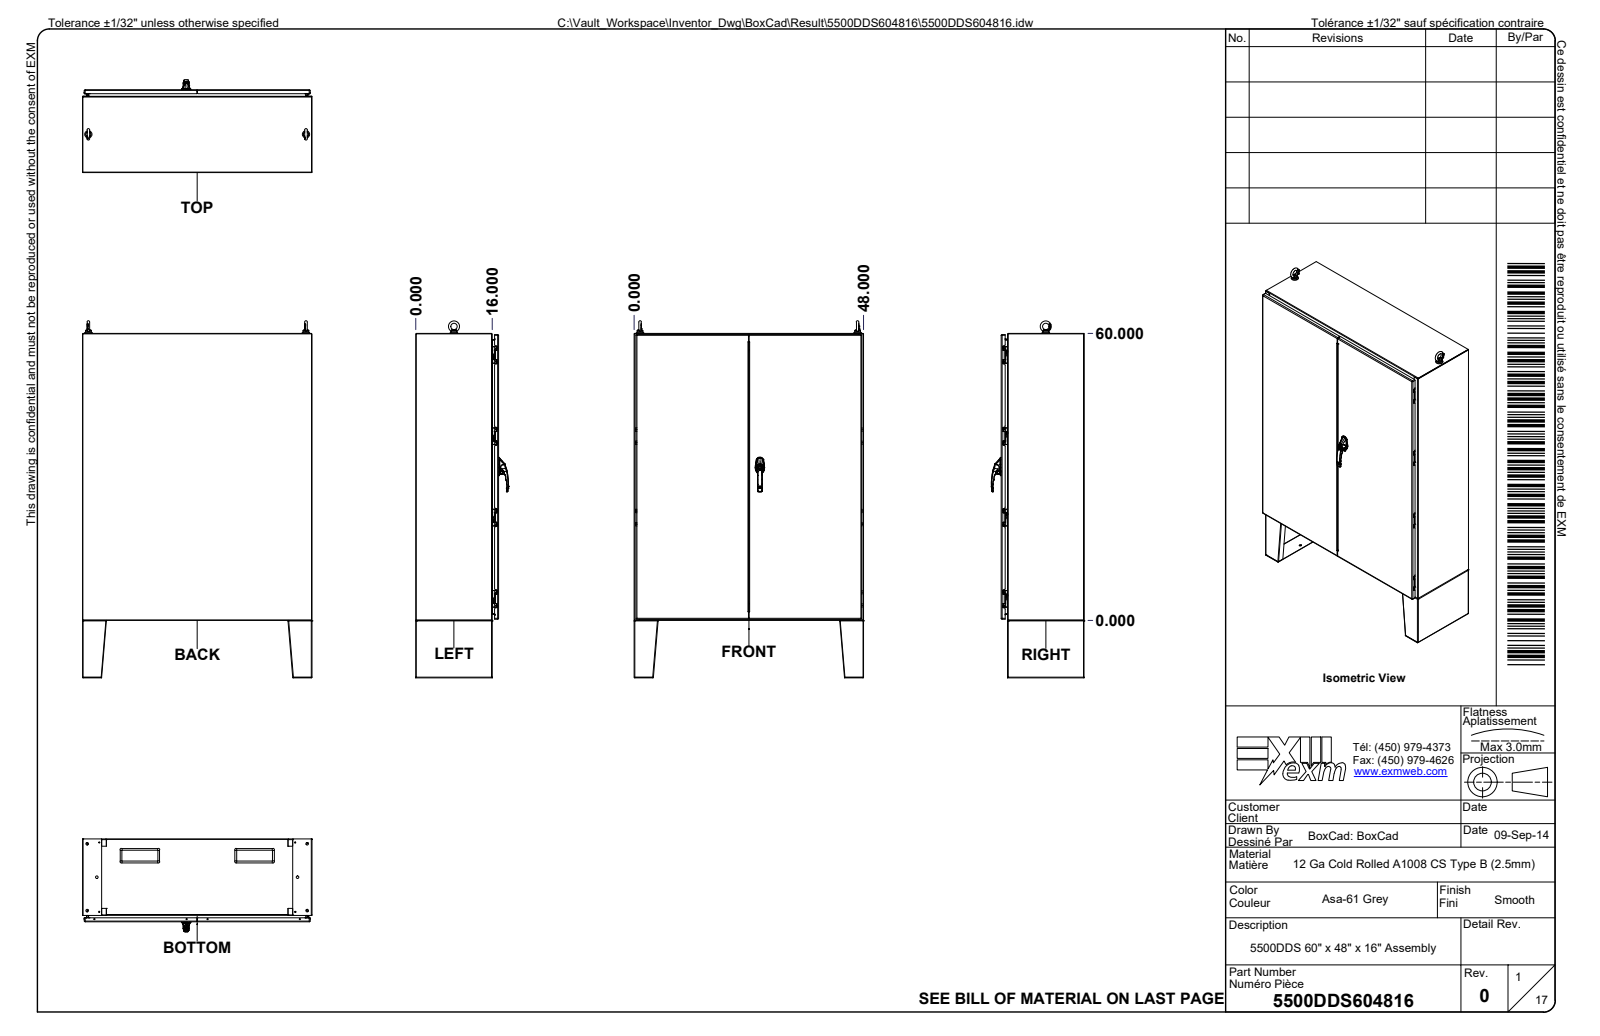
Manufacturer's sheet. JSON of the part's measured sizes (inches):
{"part_name": "5500DDS604816; 5500DDS604816B; 5500DDS604816B-P; 5500DDS604816LS-P (+8 more)", "step_written_by": "Autodesk Inventor 2024 (AUTOMOTIVE_DESIGN)", "units": "inches", "bodies": {"solids": 281, "faces": 36225, "planar": 12509, "cylindrical": 9079, "other": 14637}, "overall_size": [74.638, 48, 19.422], "volume_in3": 1357, "surface_area_in2": 31040, "round_holes": [[0.177, 288], [0.03, 41], [0.201, 26], [0.043, 16], [0.167, 16], [0.5, 14], [0.315, 12], [0.374, 12], [0.394, 12], [0.203, 8], [0.335, 8], [0.341, 8]], "round_bosses_or_shafts": [[0.272, 216], [0.03, 41], [0.232, 34], [0.039, 31], [0.289, 20], [0.177, 20], [0.39, 17], [0.874, 8]], "partial_cylinders_radius": [[0.02, 650], [0.039, 484], [0.008, 311], [0.012, 253], [0.01, 227], [0.031, 192], [0.062, 166], [0.01, 130]], "face_to_face_distances": [0.089, 17.255, 0.963, 16.292, 17.166, 17.344, 0.874, 16.381, 1.052, 16.203], "hole_center_spacings": [17, 34, 1, 0.355, 16, 18, 35, 0.394]}
